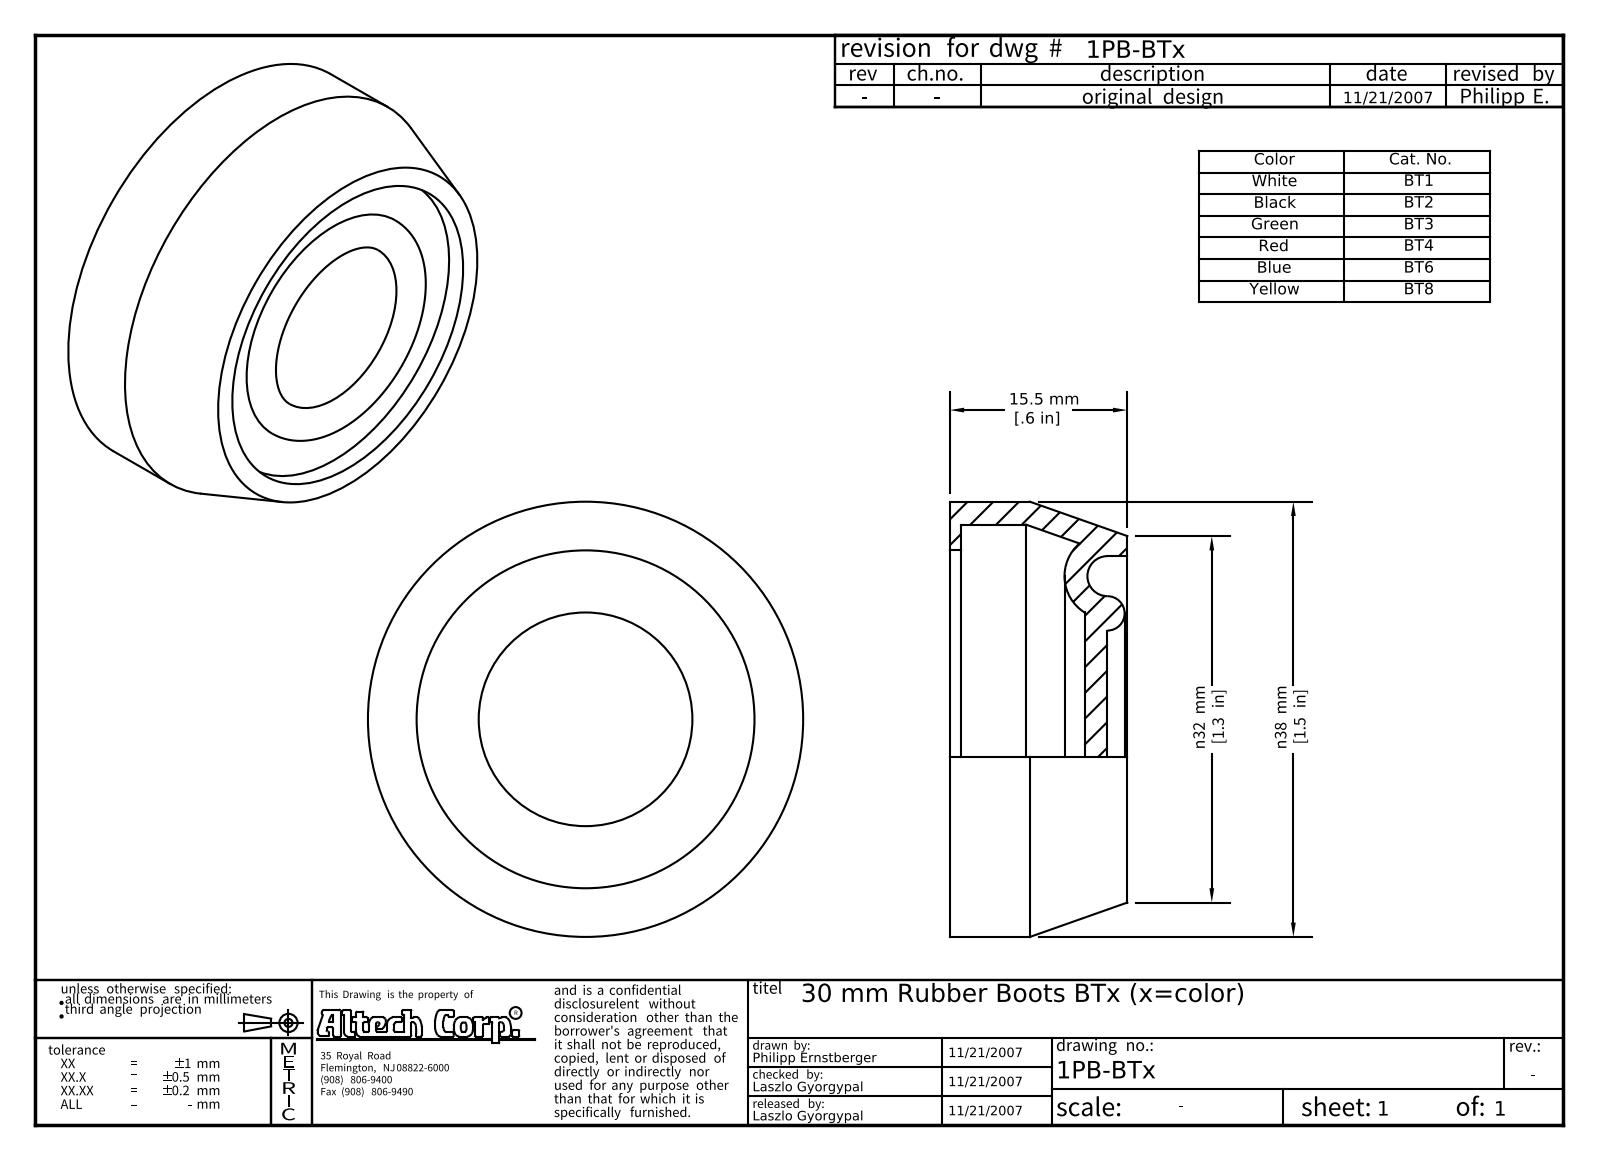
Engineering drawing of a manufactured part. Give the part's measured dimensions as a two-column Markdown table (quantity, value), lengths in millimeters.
| quantity | value |
| --- | --- |
| part name | BTx |
| STEP written by | Autodesk Inventor 2008 (AUTOMOTIVE_DESIGN) |
| units | millimeters |
| bodies | 1 solid, 14 faces (5 planar, 4 cylindrical, 5 other) |
| overall size | 38 × 38 × 15.5 |
| volume | 5 479 mm³ |
| surface area | 5 733 mm² |
| round holes (diameter × count) | 28.5 × 1, 29.5 × 1, 34 × 1 |
| round bosses / shafts (diameter × count) | 38 × 1 |
| main face-to-face distances | 11.77, 1, 10.77, 13.77, 12.77, 2, 15.5, 14.5, 3.73, 1.73 |
